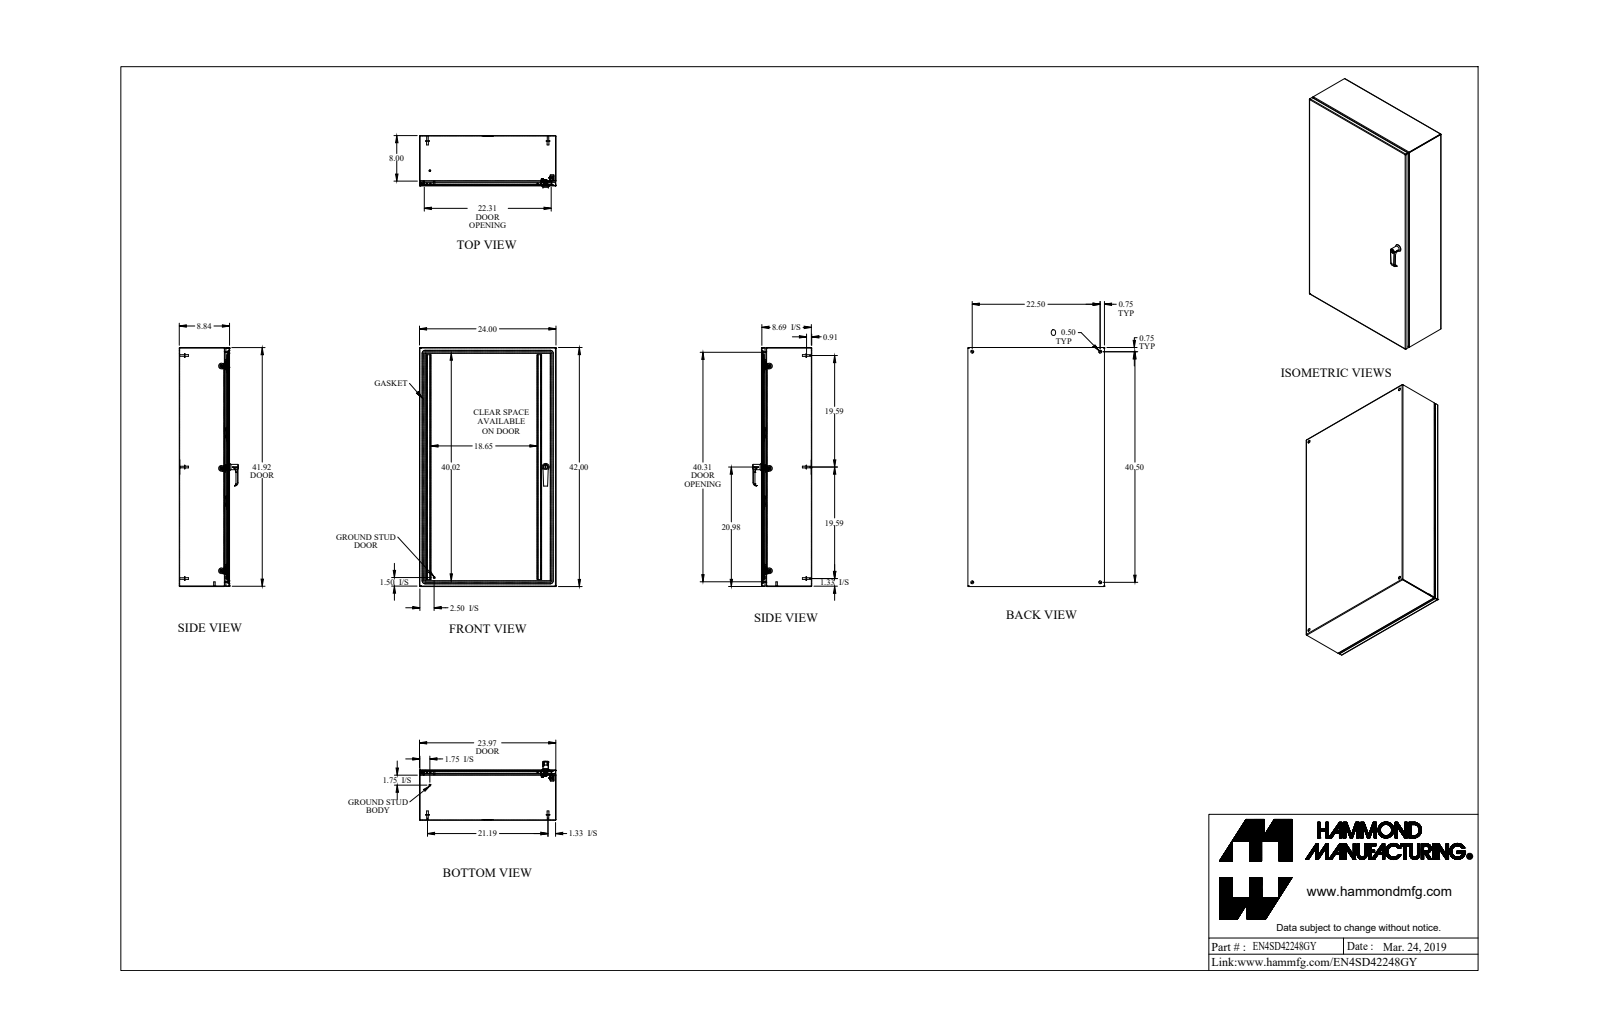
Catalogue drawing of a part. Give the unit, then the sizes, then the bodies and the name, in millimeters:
Units: millimetres
Overall size (bounding box): 1066.8 × 609.6 × 263.3
Round holes (diameter × count): ⌀4.5 ×6, ⌀12.7 ×4, ⌀5 ×3, ⌀6.4 ×3, ⌀6.7 ×3, ⌀10.5 ×3, ⌀4.4 ×2, ⌀6.1 ×2, ⌀6.5 ×2, ⌀8 ×2, ⌀10 ×2, ⌀6.1 ×1
Round bosses / shafts (diameter × count): ⌀6.4 ×7, ⌀15.9 ×6, ⌀9.5 ×6, ⌀8 ×6, ⌀6.9 ×6, ⌀4 ×6, ⌀25.4 ×3, ⌀16 ×2
Partial cylindrical surfaces — rounded edges, fillets, slot ends (radius × count): R0.9 ×20, R2.7 ×20, R0.8 ×15, R1.1 ×12, R2.1 ×12, R0.2 ×8, R1 ×8, R1.6 ×8
Main face-to-face distances: 1.8, 222.6, 220.8, 224.5, 607.8, 1065, 605.9, 609.6, 1063.1, 1066.8
Hole centre spacings: 20, 456.7, 457.2, 571.5, 913.6, 1028.7, 1176.8, 0.3
Volume: 4 372 000 mm³ · Surface area: 4 772 000 mm²
Bodies: 53 solids, 1457 faces (632 planar, 538 cylindrical, 287 other)
Part name (STEP PRODUCT): EN4SD42248GY_Default
STEP written by: SolidWorks 2019 (CONFIG_CONTROL_DESIGN)
